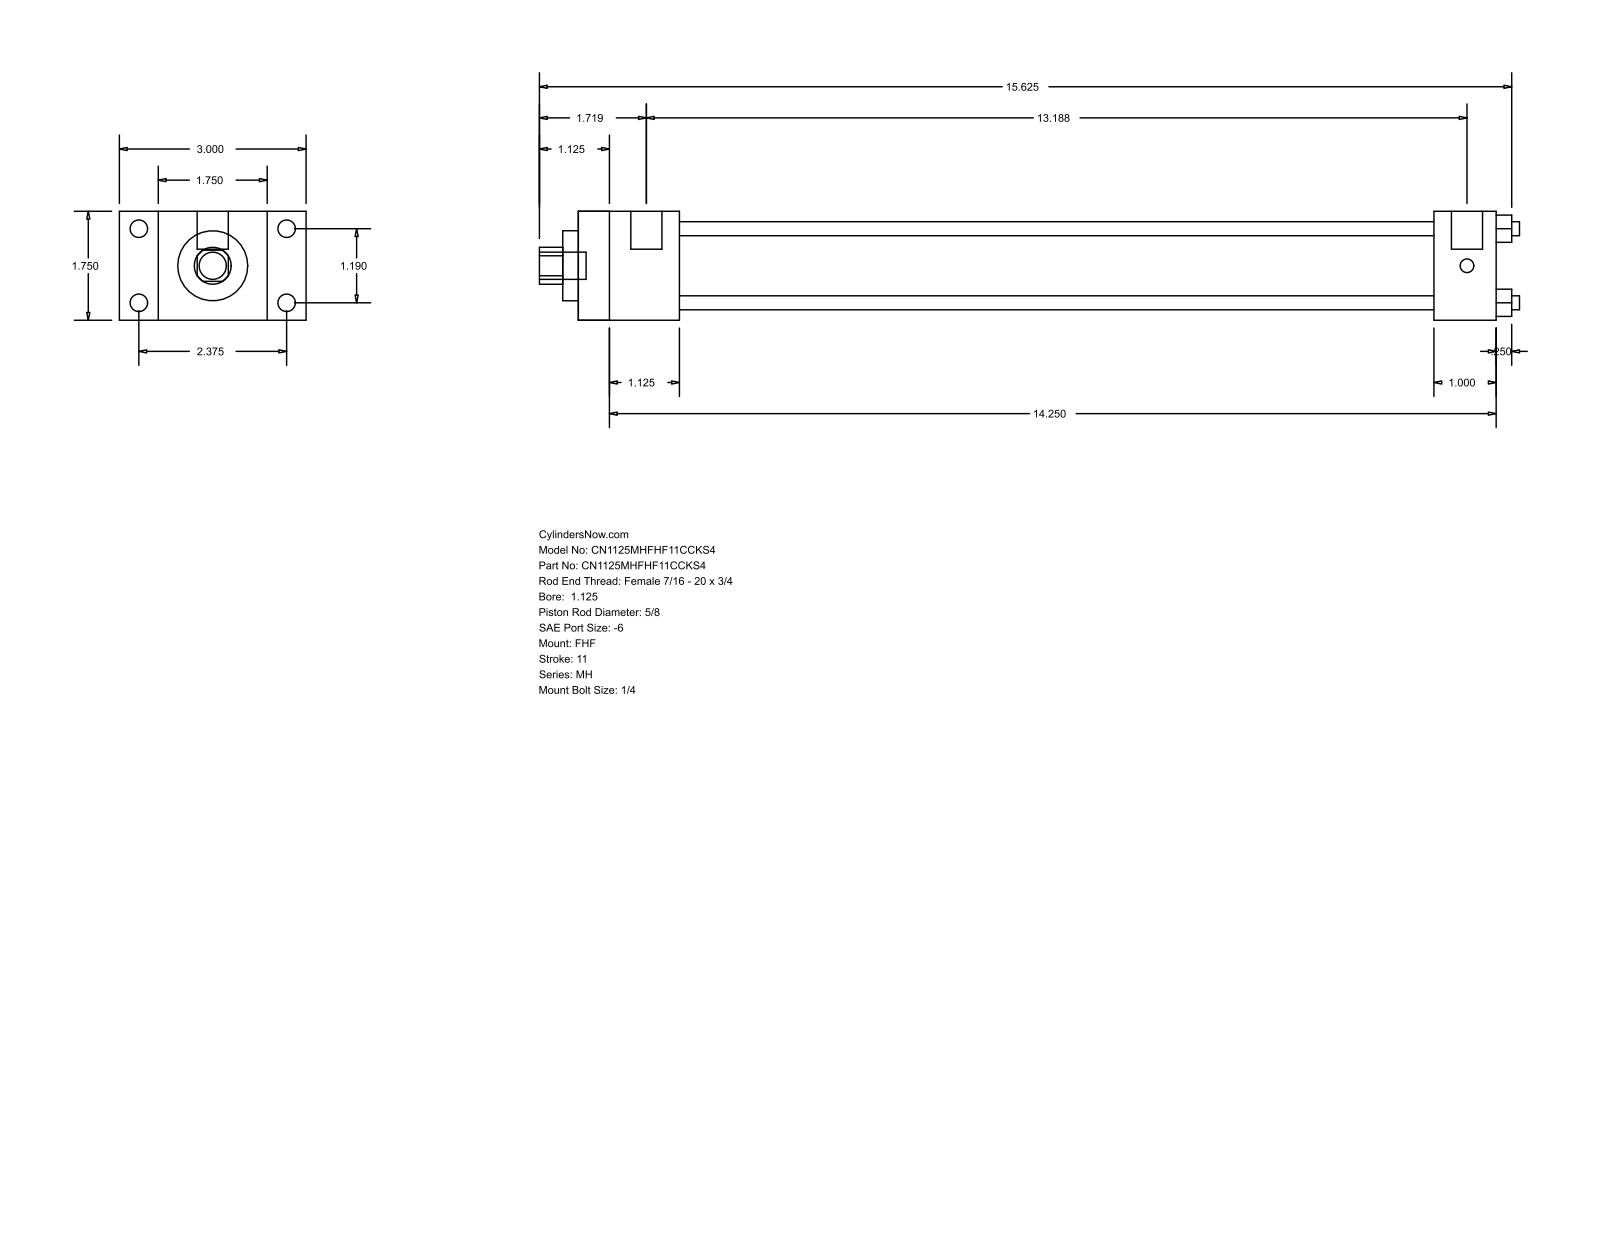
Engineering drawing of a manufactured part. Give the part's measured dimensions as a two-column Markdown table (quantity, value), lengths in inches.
| quantity | value |
| --- | --- |
| part name | MH_FHF__0112_0.625 |
| STEP written by | GSSL Pune (CONFIG_CONTROL_DESIGN) |
| units | inches |
| bodies | 0 solids, 88 faces (60 planar, 28 cylindrical, 0 other) |
| overall size | 15.75 × 3 × 1.75 |
| round holes (diameter × count) | 0.225 × 4, 0.625 × 1, 1.125 × 1, 1.375 × 1 |
| round bosses / shafts (diameter × count) | 0.281 × 4, 0.219 × 4, 0.5 × 2, 0.437 × 1 |
| partial cylindrical surfaces (radius × count) | 0.297 × 1 |
| main face-to-face distances | 1.75, 0.625, 2.375, 1.625, 3, 14.75, 13.125, 13.75, 12.125, 1 |
| hole center spacings | 0.841, 1.19, 1.683 |
